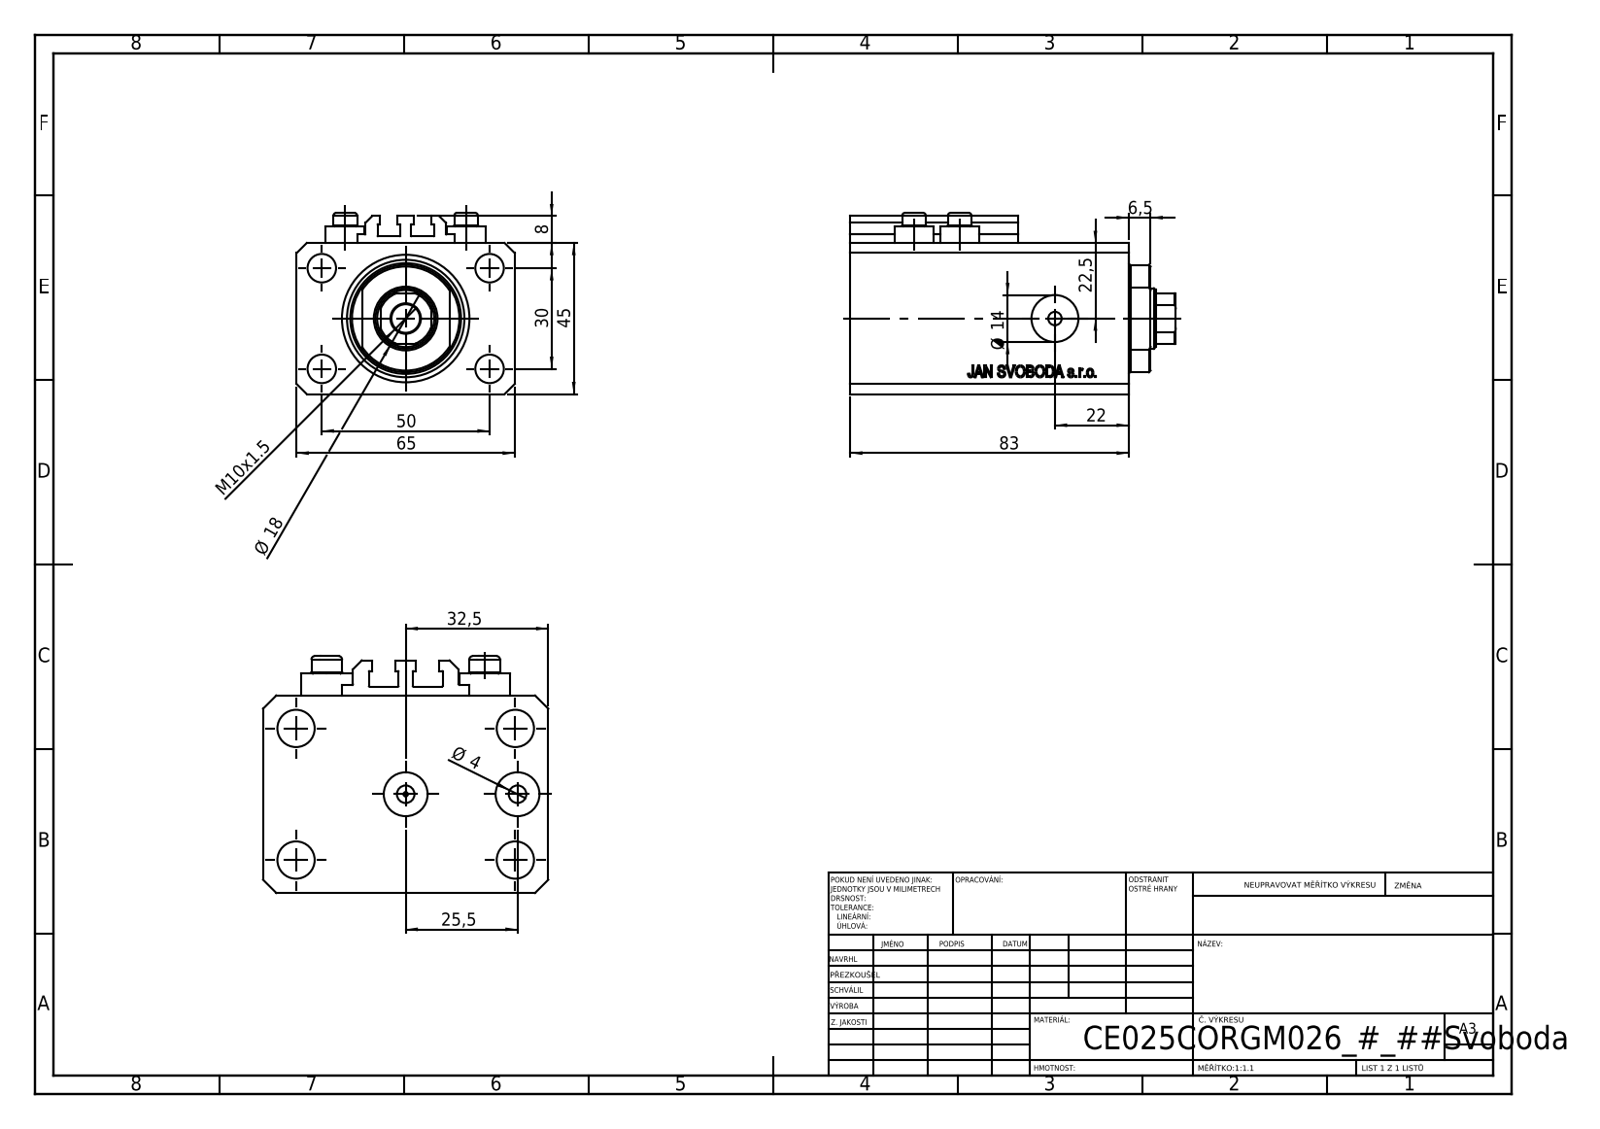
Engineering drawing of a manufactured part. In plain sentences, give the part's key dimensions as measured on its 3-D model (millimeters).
The part is named "V250CE_C_VCP; V250CE_C_Body; ALLEN BOLT V250CE; V250CE_VC_C". Its 3-D file was written by "SolidWorks 2019 (CONFIG_CONTROL_DESIGN)". It is 8 solids with 1042 faces: 504 planar, 92 cylindrical and 446 other. Overall it measures 97 by 65 by 54 millimeters. Its volume is 226 920 cubic millimeters and its surface area 61 014 square millimeters. Round holes: 8 of diameter 4, 5 of diameter 8.5, 2 of diameter 10, 2 of diameter 14, 1 of diameter 1.25, 1 of diameter 18, 1 of diameter 25, 1 of diameter 38. Round bosses or shafts: 4 of diameter 11.6, 4 of diameter 7. Partial cylindrical surfaces (rounded edges, fillets, slot ends): 10 of radius 0.2, 1 of radius 8.5, 1 of radius 16. The main face-to-face distances are 45, 65, 14, 83, 69, 47, 6.9, 62.1, 76.1, 3. The hole center spacings are 29.15, 13.6, 15.01, 30, 36, 38.48, 50, 52.68.
